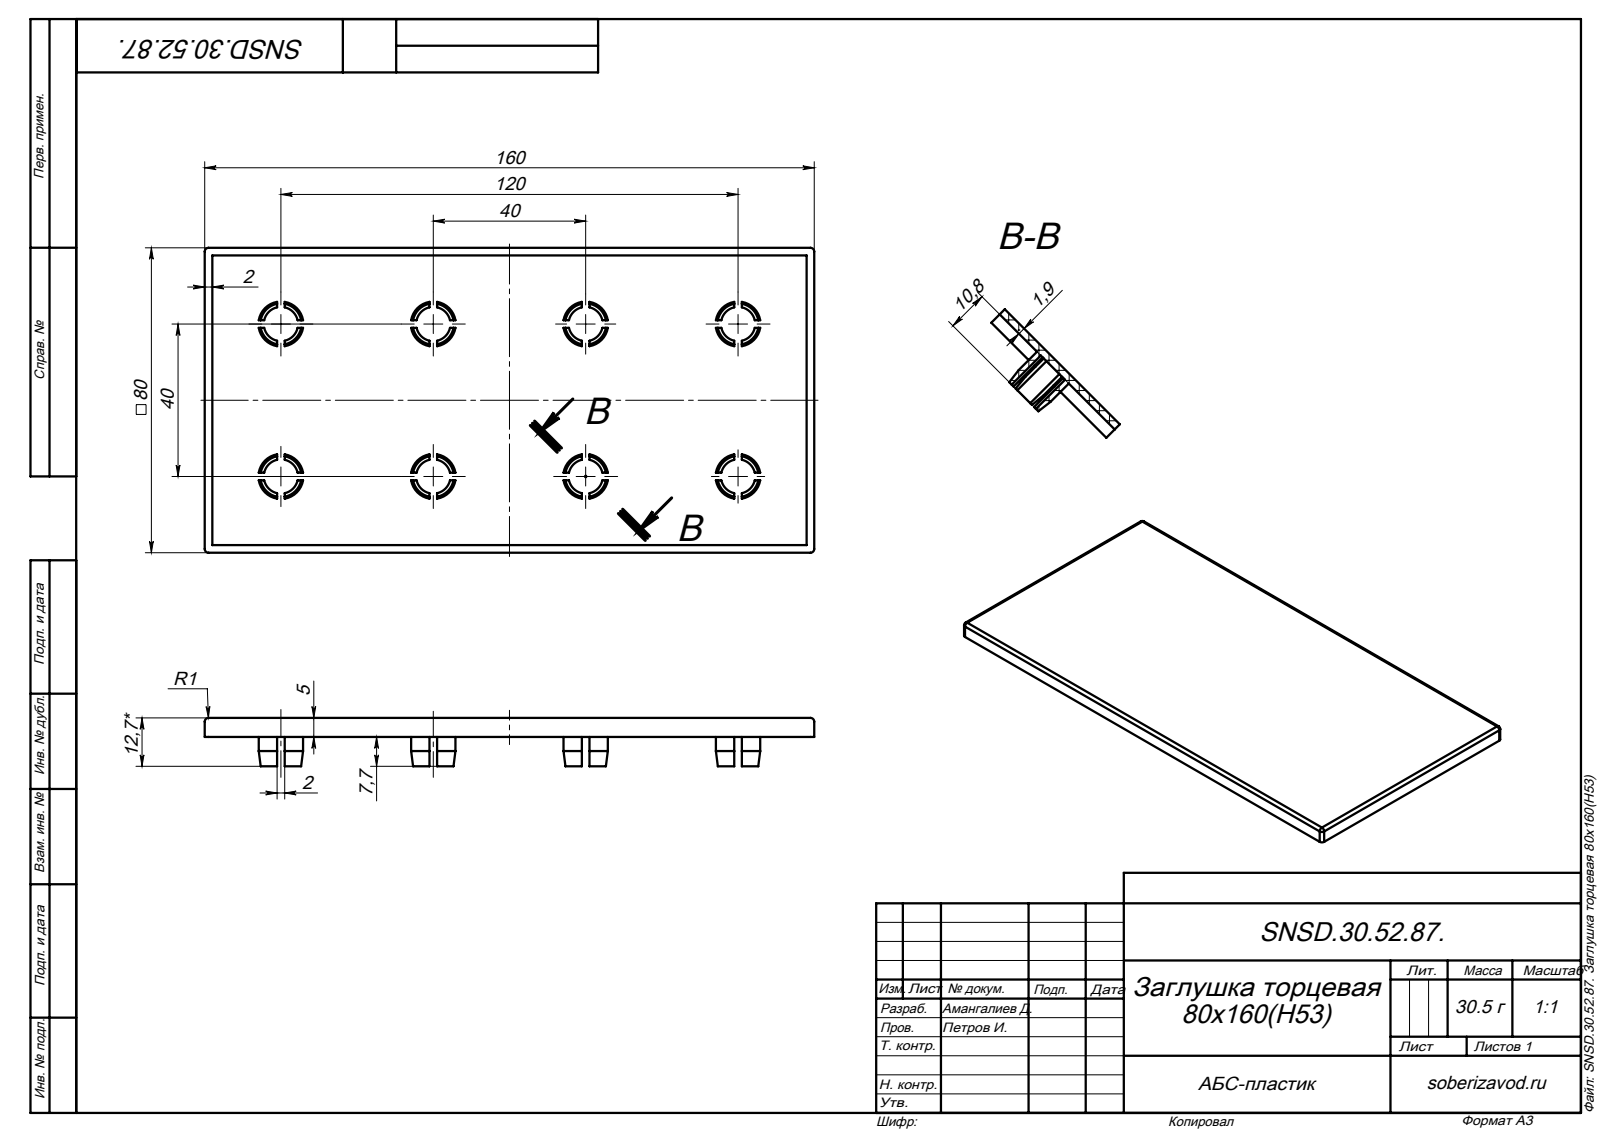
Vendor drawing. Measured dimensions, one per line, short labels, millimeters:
name: SNSD.30.52.87. Заглушка торцевая 80x160(H53)
written by: SolidWorks 2014 (AUTOMOTIVE_DESIGN)
unit: mm
bodies: 1 solid, 215 faces (107 planar, 72 cylindrical, 36 other)
size: 160 × 80 × 12.7
volume: 29 894 mm³; area: 34 245 mm²
rounds: 8× R1, 8× R4.5, 8× R5.9
face distances: 1.9, 2, 78, 3.1, 5, 80, 19, 59, 40, 76
